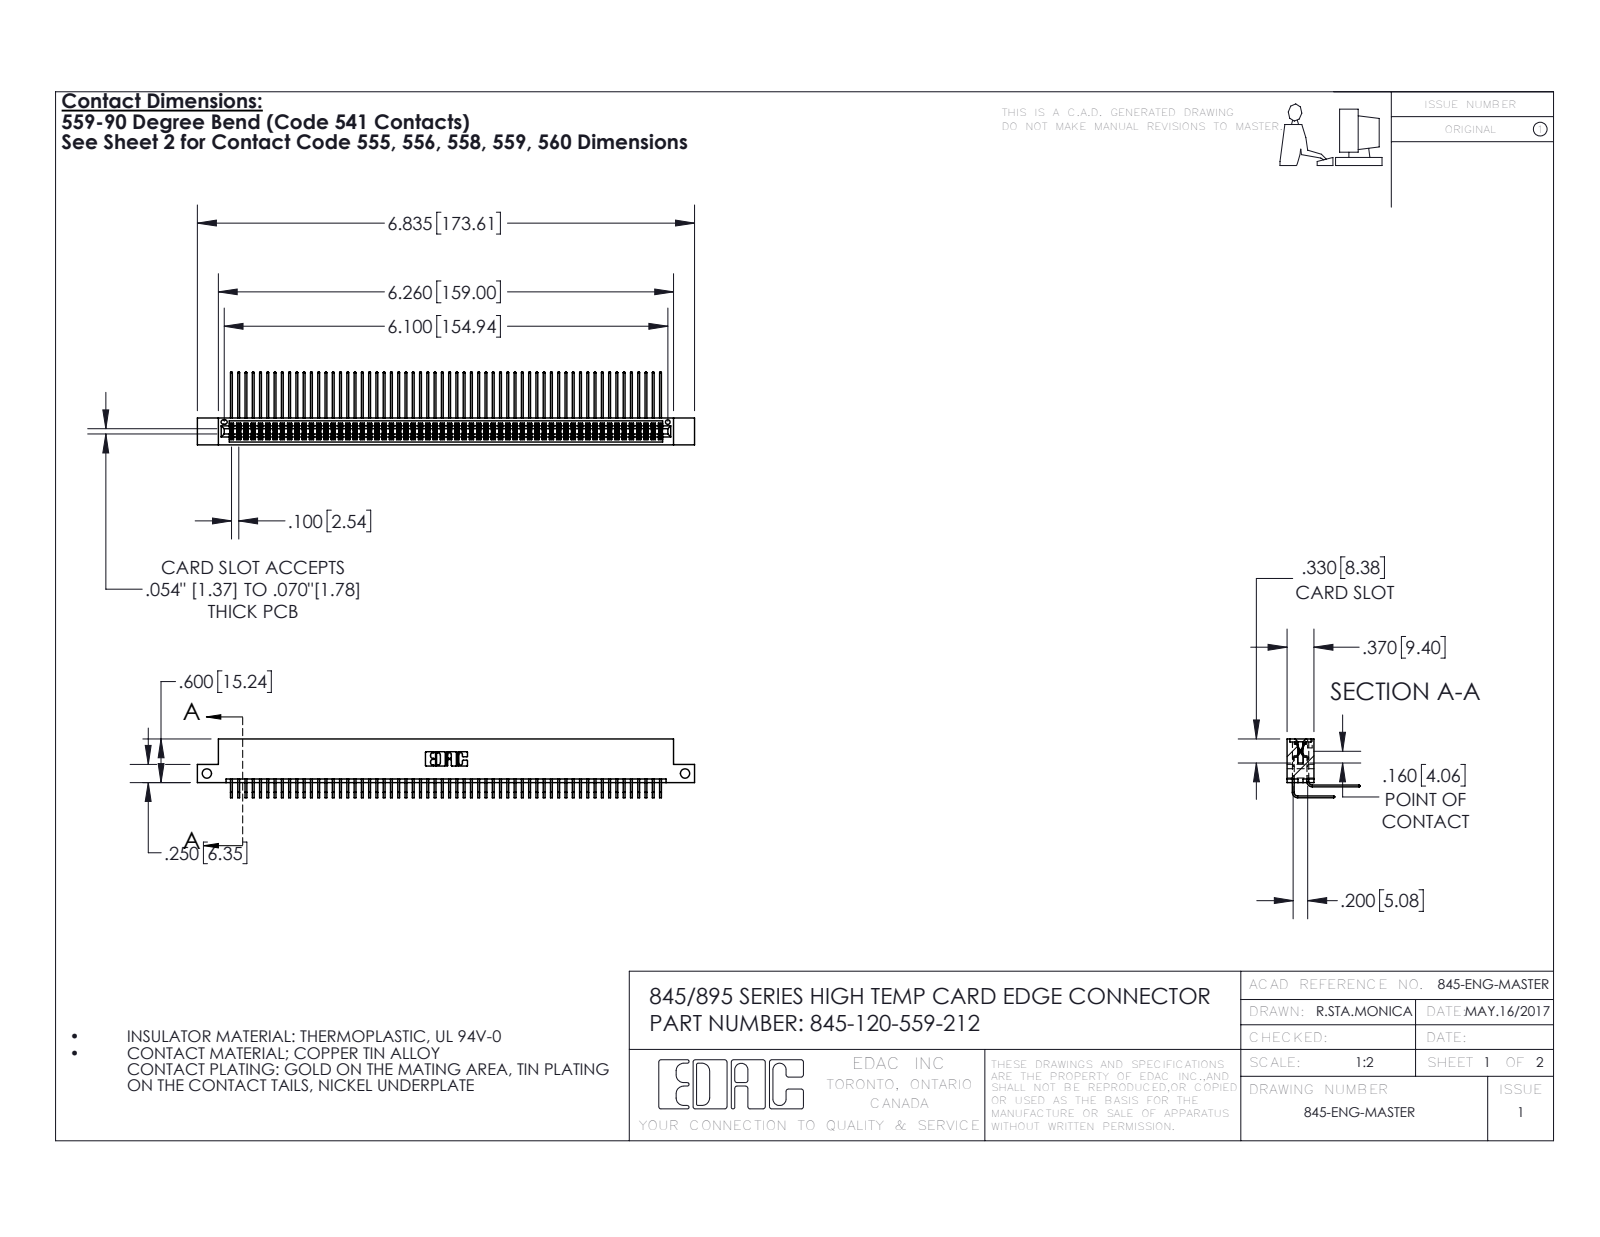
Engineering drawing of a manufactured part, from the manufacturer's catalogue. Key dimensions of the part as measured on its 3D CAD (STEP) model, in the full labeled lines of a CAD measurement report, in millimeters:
Part name (STEP PRODUCT): 345-292-001_558 559 Tail - 1; 845 Part_Flush Mounting Lugs - Side Mount; 845-120-559-212; 345-292-001_559 Tail - 2
STEP written by: SolidWorks 2016 (CONFIG_CONTROL_DESIGN)
Units: millimetres
Bodies: 121 solids, 6366 faces (4280 planar, 2086 cylindrical, 0 other)
Overall size (bounding box): 173.6 × 25.5 × 20.5
Volume: 17 630 mm³ · Surface area: 29 540 mm²
Round holes (diameter × count): ⌀3.3 ×2, ⌀1.6 ×1
Partial cylindrical surfaces — rounded edges, fillets, slot ends (radius × count): R0.2 ×239, R0.3 ×22, R0.2 ×6, R0.8 ×6, R0.7 ×3, R0.4 ×2, R0.5 ×2, R0.6 ×2
Main face-to-face distances: 1.8, 7.6, 5.1, 9.4, 2.5, 6.9, 0.6, 5.7, 4.4, 3.8
Hole centre spacings: 167
